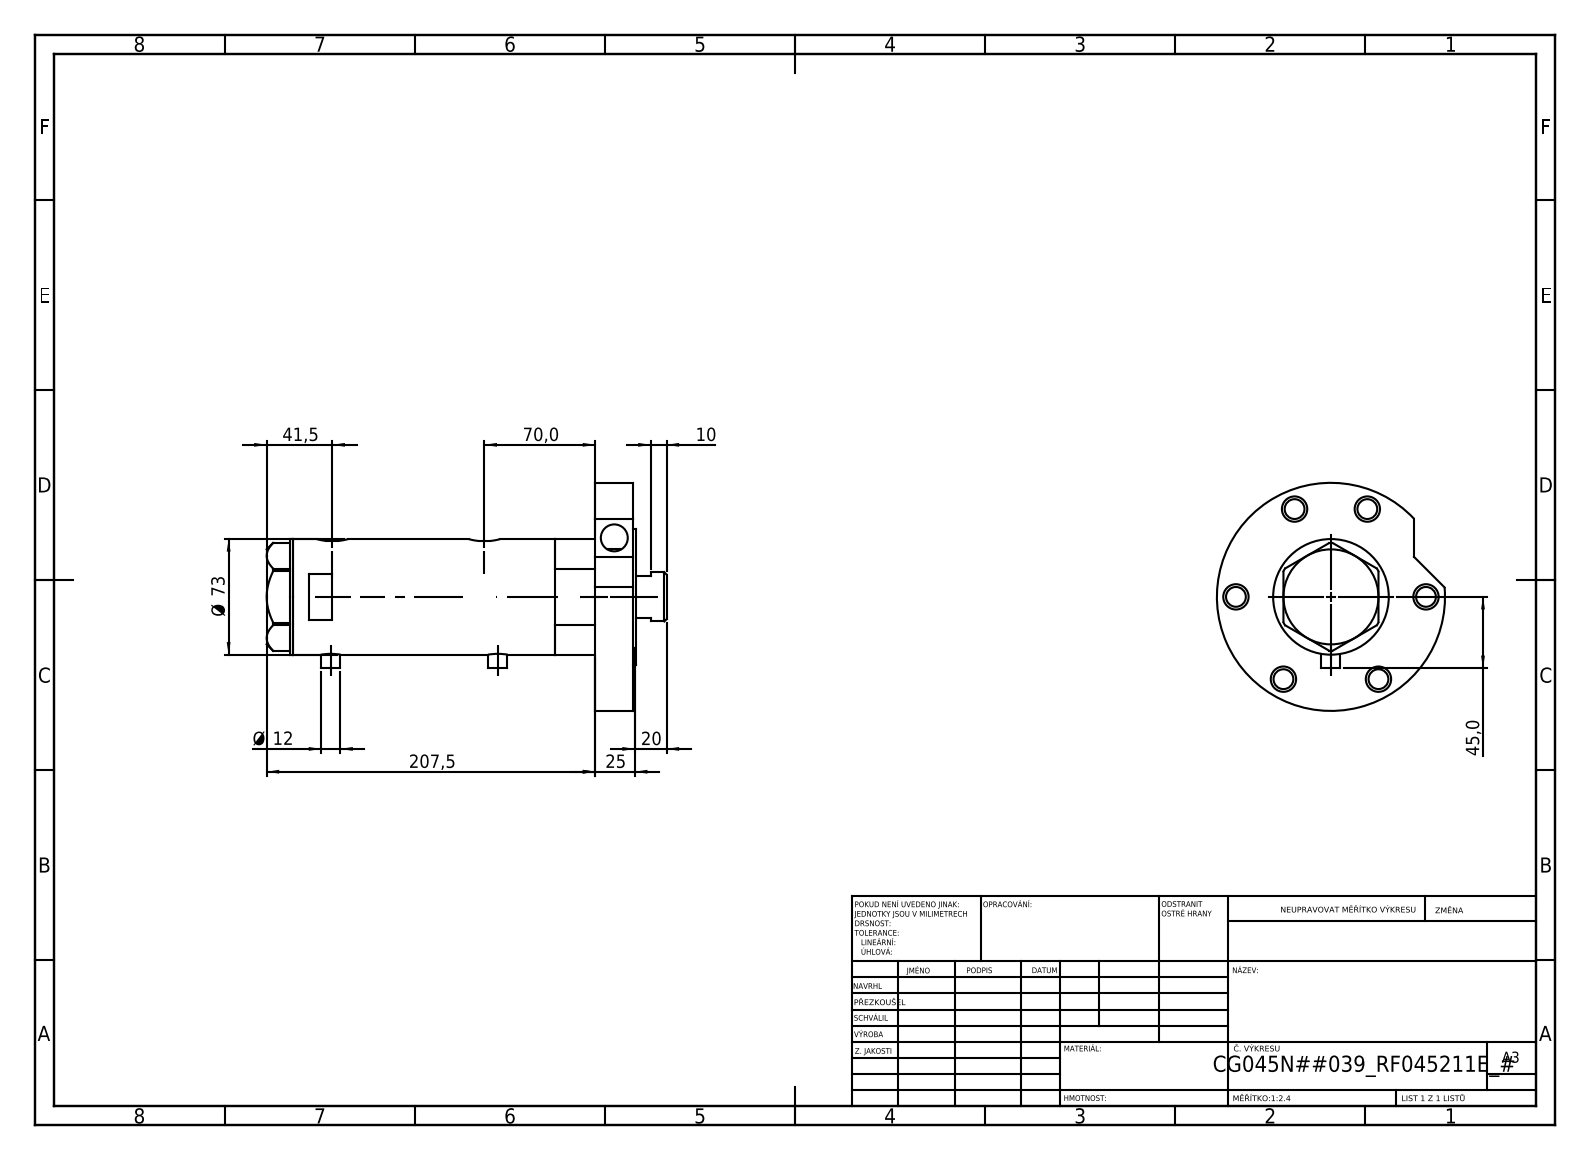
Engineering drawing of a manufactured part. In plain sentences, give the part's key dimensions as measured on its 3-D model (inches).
The part is named "V270CG_VC; V270CG_MIDDLE; V270CG_RF211E; V270CG_BACK (+1 more)". Its 3-D file was written by "SolidWorks 2019 (CONFIG_CONTROL_DESIGN)". It is 5 solids with 164 faces: 60 planar, 84 cylindrical and 20 other. Overall it measures 9.941 by 5.669 by 5.669 inches. Its volume is 71.34 cubic inches and its surface area 313 square inches. Round holes: 8 of diameter 0.492, 6 of diameter 0.63, 2 of diameter 0.518, 1 of diameter 0.413, 1 of diameter 0.669, 1 of diameter 1.26, 1 of diameter 1.319, 1 of diameter 1.772, 1 of diameter 1.89, 1 of diameter 2.362, 1 of diameter 2.52. Round bosses or shafts: 2 of diameter 0.472, 1 of diameter 5.669, 1 of diameter 3.386, 1 of diameter 2.874, 1 of diameter 2.283, 1 of diameter 1.22. Partial cylindrical surfaces (rounded edges, fillets, slot ends): 2 of radius 0.394. The main face-to-face distances are 0.945, 7.52, 1.024, 3.74, 0.079, 8.465, 8.543, 4.764, 2.756, 3.701. The hole center spacings are 2.362, 2.625, 3.928, 4.091, 4.237, 4.714, 0.039, 0.335.
